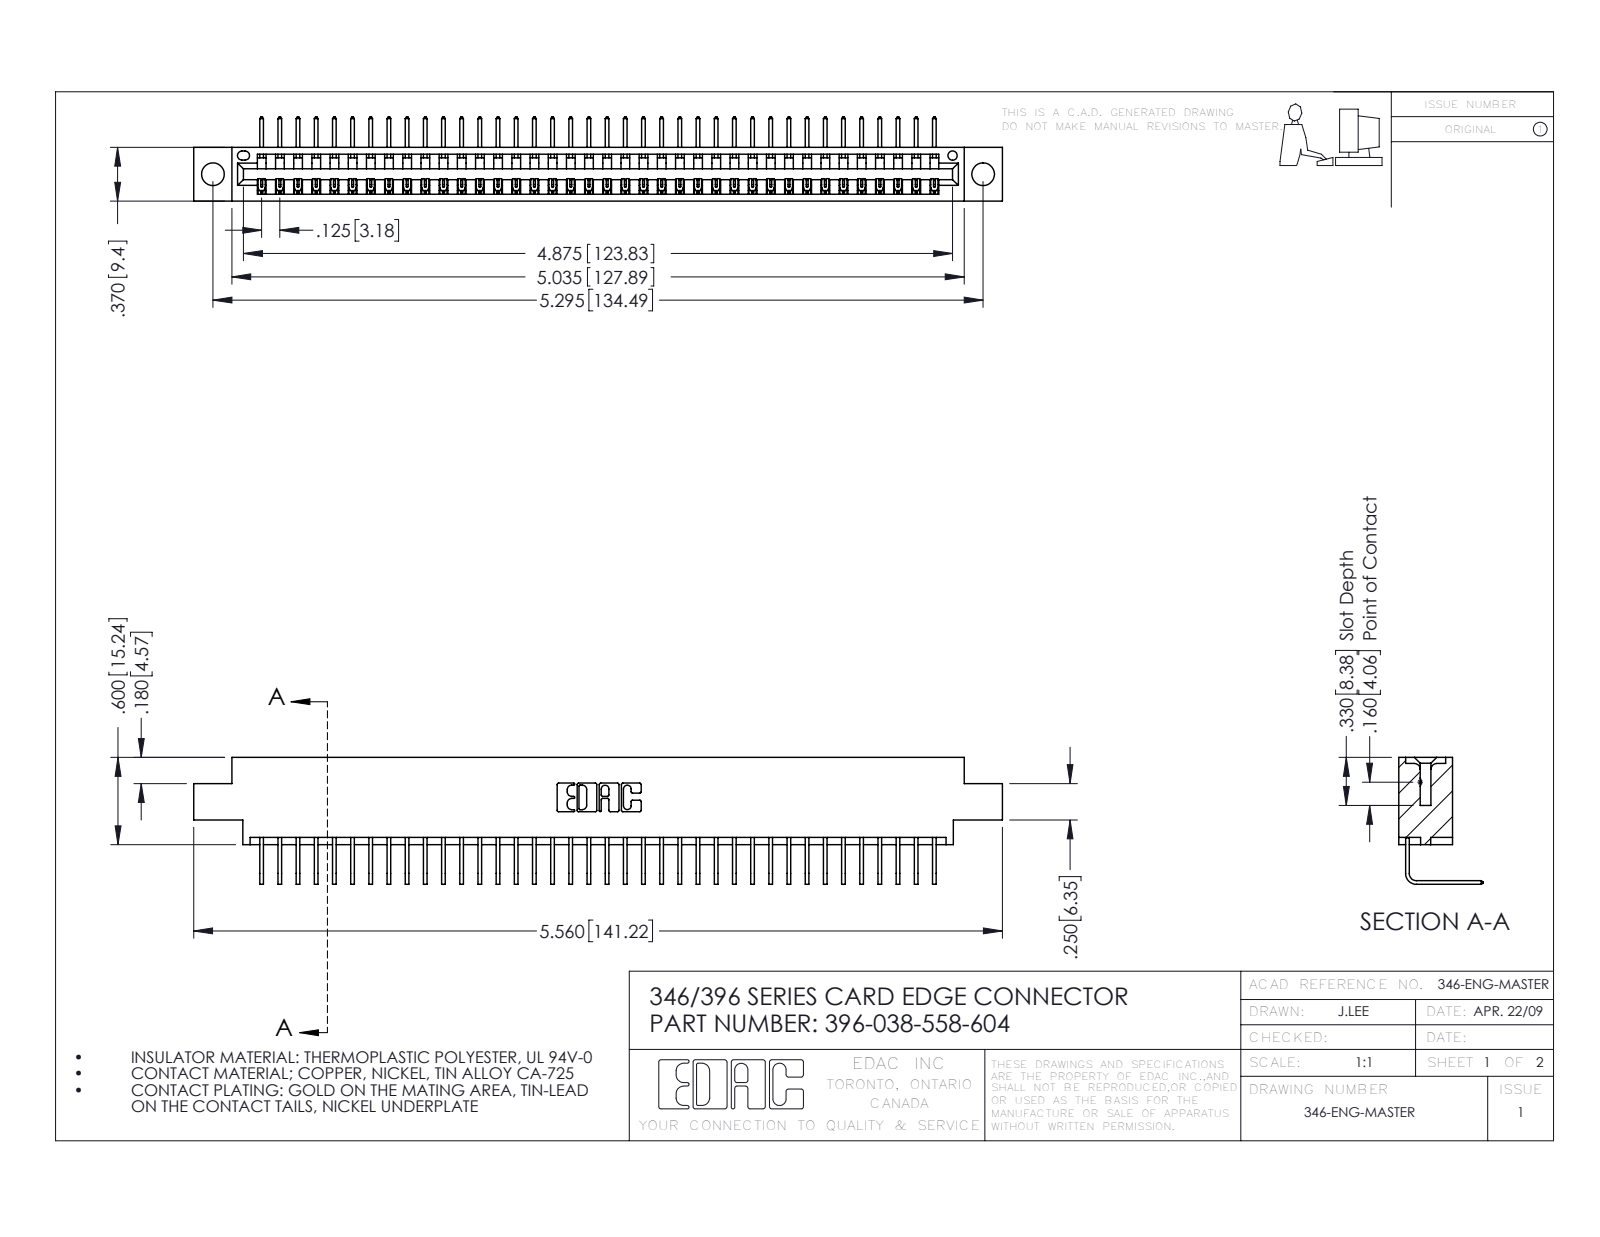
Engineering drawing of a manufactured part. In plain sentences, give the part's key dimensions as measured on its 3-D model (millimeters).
The part is named "346 Part_0.170 Offset - 0.156 Dia-TH; 396-038-558-604; 345-292-001_558 Tail - 2". Its 3-D file was written by "SolidWorks 2016 (CONFIG_CONTROL_DESIGN)". It is 39 solids with 2406 faces: 1676 planar, 730 cylindrical and 0 other. Overall it measures 141.2 by 22.2 by 14.7 millimeters. Its volume is 13 400 cubic millimeters and its surface area 17 390 square millimeters. Round holes: 2 of diameter 4, 1 of diameter 1.6. Partial cylindrical surfaces (rounded edges, fillets, slot ends): 76 of radius 0.2, 22 of radius 0.3, 6 of radius 0.2, 6 of radius 0.8, 3 of radius 0.7, 2 of radius 0.8, 2 of radius 1, 1 of radius 0.4. The main face-to-face distances are 8.2, 1.2, 9.4, 6.4, 7.6, 0.6, 1.8, 3.8, 5.6, 2.5. The hole center spacings are 6.2, 129.2, 134.5.
